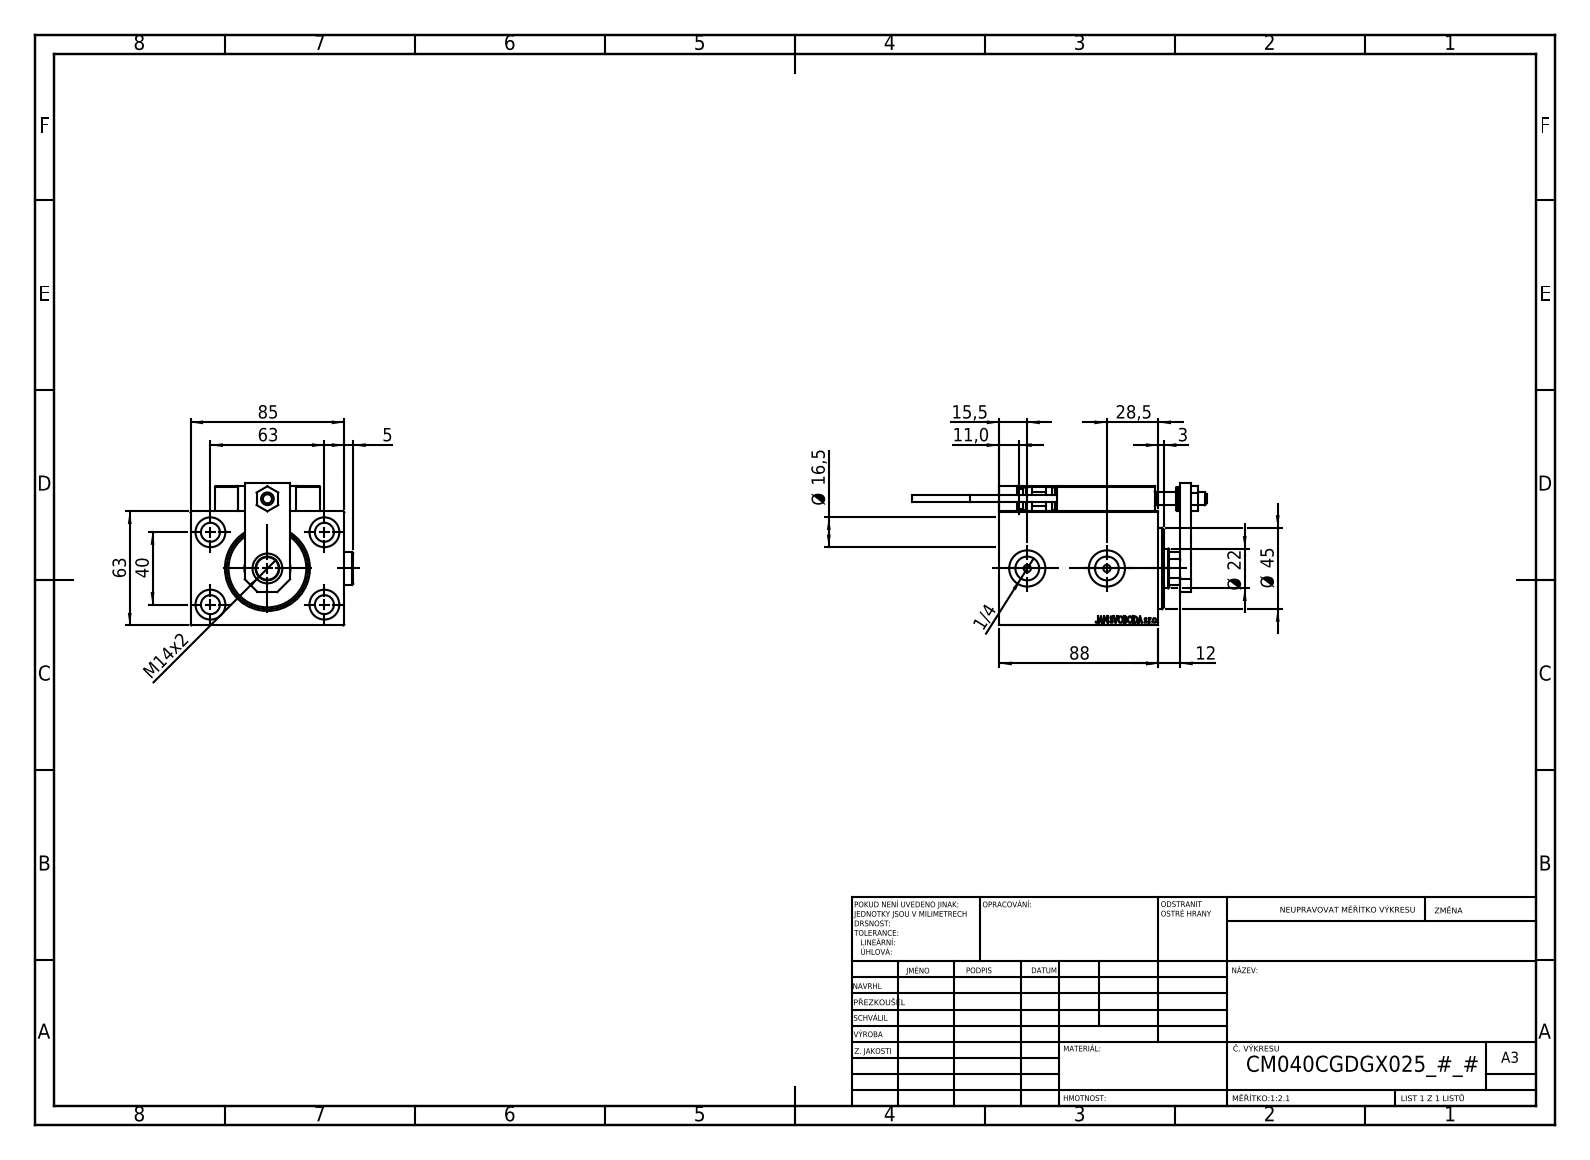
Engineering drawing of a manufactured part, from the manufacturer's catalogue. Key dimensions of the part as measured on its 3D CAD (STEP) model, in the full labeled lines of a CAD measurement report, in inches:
Part name (STEP PRODUCT): KONCOVKA; ZARAZKA; V450CM_C_VCP; V450CM_VC_B (+8 more)
STEP written by: SolidWorks 2019 (CONFIG_CONTROL_DESIGN)
Units: inches
Bodies: 25 solids, 1336 faces (594 planar, 204 cylindrical, 538 other)
Overall size (bounding box): 6.406 × 3.539 × 3.091
Volume: 27.82 in³ · Surface area: 162.4 in²
Round holes (diameter × count): ⌀0.157 ×6, ⌀0.315 ×5, ⌀0.65 ×5, ⌀0.126 ×4, ⌀0.413 ×4, ⌀0.197 ×2, ⌀0.518 ×2, ⌀0.787 ×2, ⌀0.276 ×1, ⌀0.492 ×1, ⌀0.866 ×1, ⌀1.004 ×1
Round bosses / shafts (diameter × count): ⌀0.709 ×2, ⌀0.197 ×2, ⌀0.15 ×2, ⌀0.512 ×1, ⌀0.433 ×1
Partial cylindrical surfaces — rounded edges, fillets, slot ends (radius × count): R0.012 ×30, R0.118 ×2, R0.413 ×1
Main face-to-face distances: 2.48, 0.472, 3.346, 2.992, 3.465, 0.551, 3.031, 0.984, 0.591, 0.709
Hole centre spacings: 1.469, 0.448, 0.787, 1.165, 1.169, 1.42, 1.438, 1.575
